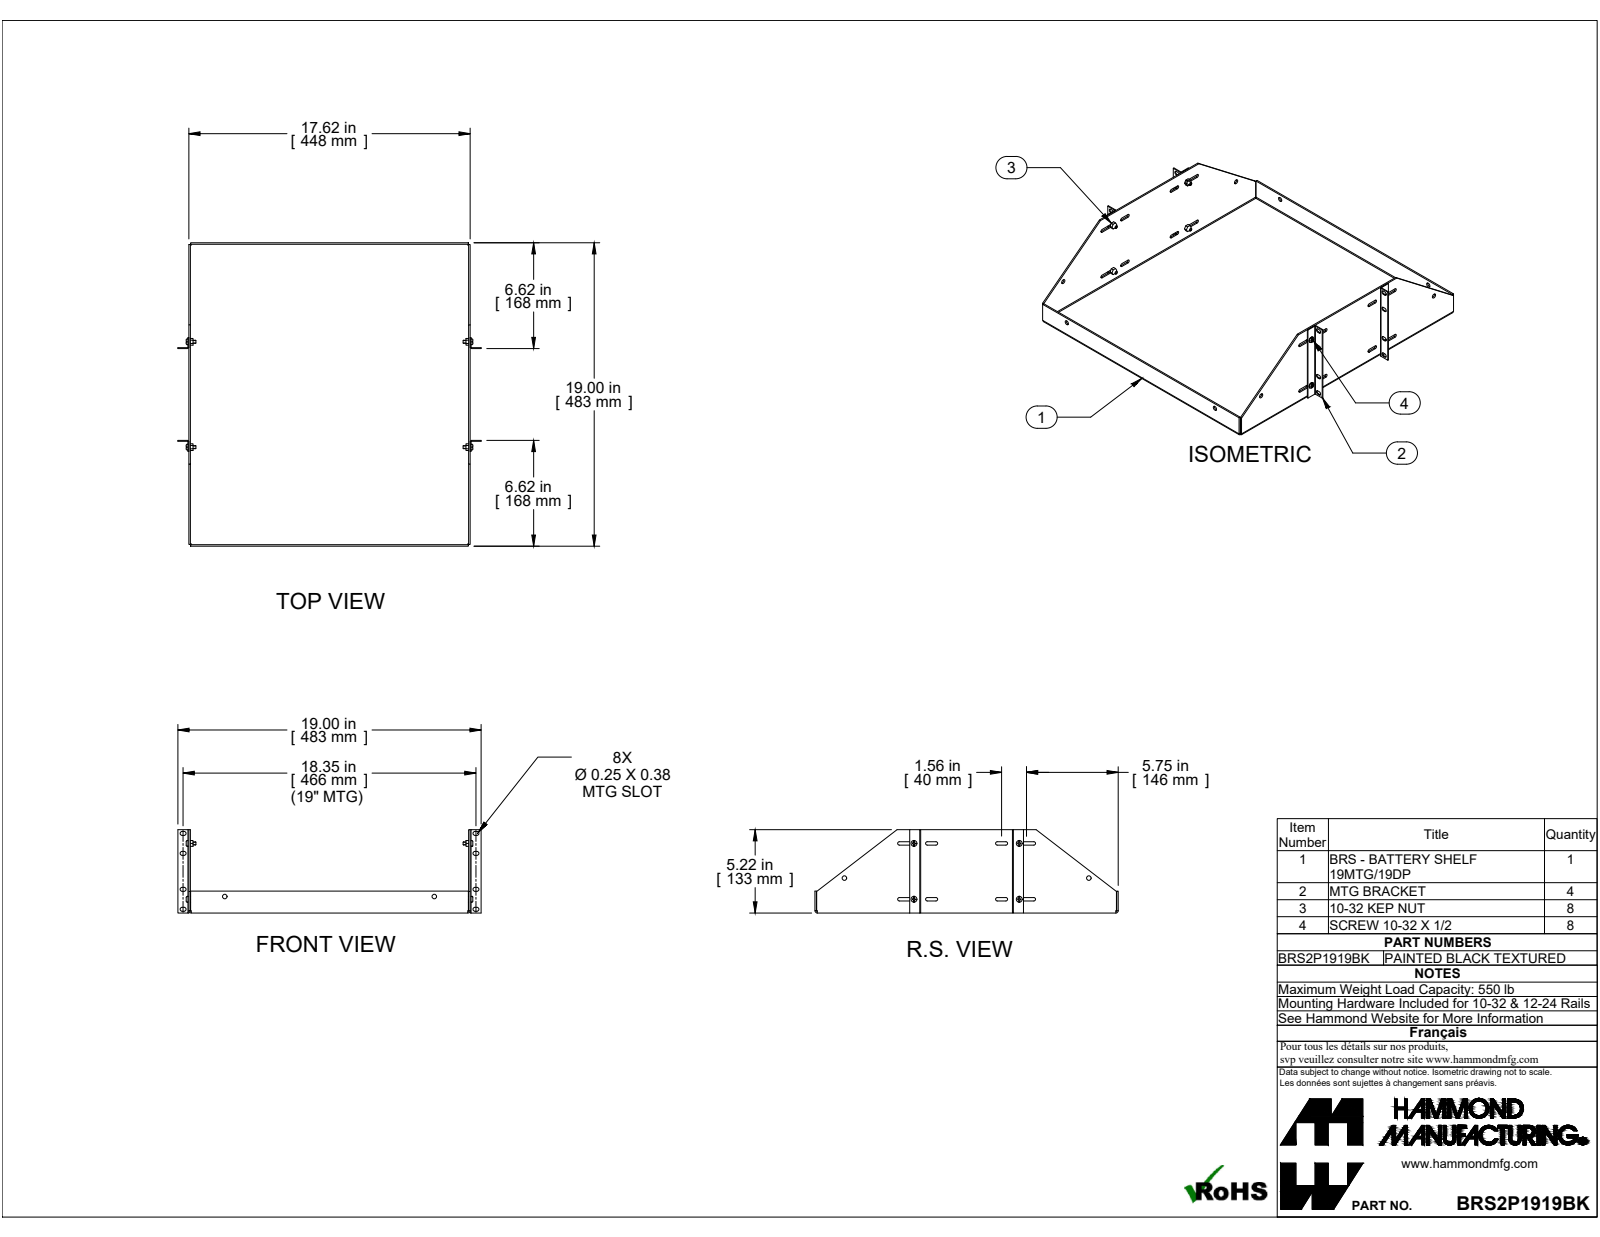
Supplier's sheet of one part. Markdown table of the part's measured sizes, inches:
| quantity | value |
| --- | --- |
| part name | BRS2P1919BK |
| STEP written by | SolidWorks 2019 (CONFIG_CONTROL_DESIGN) |
| units | inches |
| bodies | 21 solids, 466 faces (322 planar, 120 cylindrical, 24 other) |
| overall size | 19 × 19 × 5.218 |
| volume | 51.76 in³ |
| surface area | 1 129 in² |
| round holes (diameter × count) | 0.156 × 4, 0.213 × 4, 0.281 × 4 |
| round bosses / shafts (diameter × count) | 0.37 × 4, 0.19 × 4 |
| partial cylindrical surfaces (radius × count) | 0.125 × 16, 0.106 × 12, 0.029 × 4, 0.048 × 4, 0.086 × 4, 0.143 × 4 |
| main face-to-face distances | 0.095, 17.53, 0.095, 17.625, 17.435, 18.905, 0.057, 19, 18.81, 0.152 |
| hole center spacings | 3.5, 4.556, 4.869, 6.597, 7.468, 11.035, 11.168, 13.125 |
